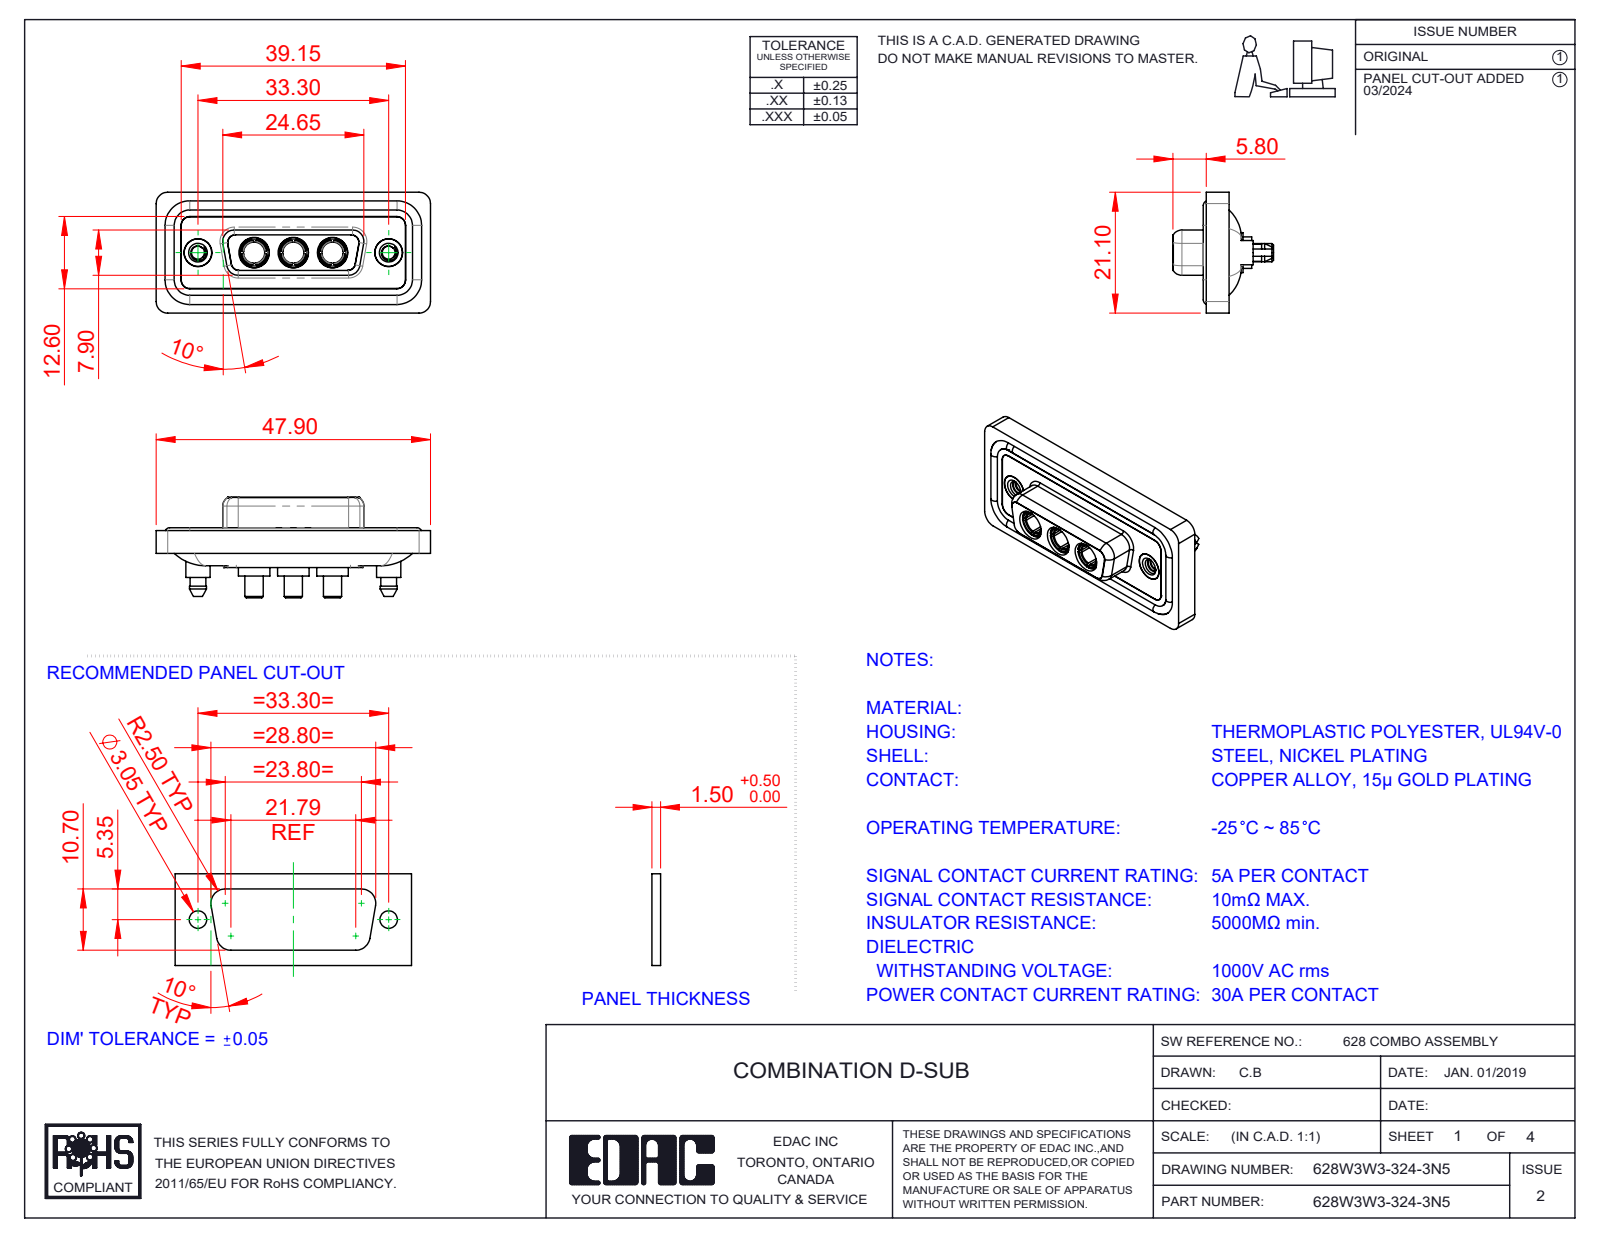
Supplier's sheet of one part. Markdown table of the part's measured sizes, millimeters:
| quantity | value |
| --- | --- |
| part name | 628Combo Housing_3W3; 628Combo Threaded Boardlock_5; 628W3W3-324-3N5; 628Combo Waterproof Housing_15 Contacts (+3 more) |
| STEP written by | SolidWorks 2023 (CONFIG_CONTROL_DESIGN) |
| units | millimeters |
| bodies | 13 solids, 658 faces (208 planar, 289 cylindrical, 161 other) |
| overall size | 47.9 × 21.1 × 17.55 |
| volume | 6 181 mm³ |
| surface area | 10 085 mm² |
| round holes (diameter × count) | 4.85 × 5, 3.7 × 3, 5.3 × 3, 2.26 × 2, 4 × 2, 4.05 × 2, 5 × 2 |
| round bosses / shafts (diameter × count) | 1.6 × 4, 5.5 × 3, 5.2 × 3, 4.96 × 3, 4.75 × 3, 3.75 × 3, 3.2 × 3, 5.4 × 2 |
| partial cylindrical surfaces (radius × count) | 1.5 × 24, 2 × 20, 1.35 × 12, 1.6 × 10, 0.25 × 4, 0.5 × 4, 0.6 × 4, 0.65 × 4 |
| main face-to-face distances | 0.4, 1.8, 1.6, 0.5, 7.45, 1.1, 2.9, 5.65, 7.05, 6.6 |
| hole center spacings | 6.85, 9.8, 16.65, 23.5, 13.7, 33.3 |
